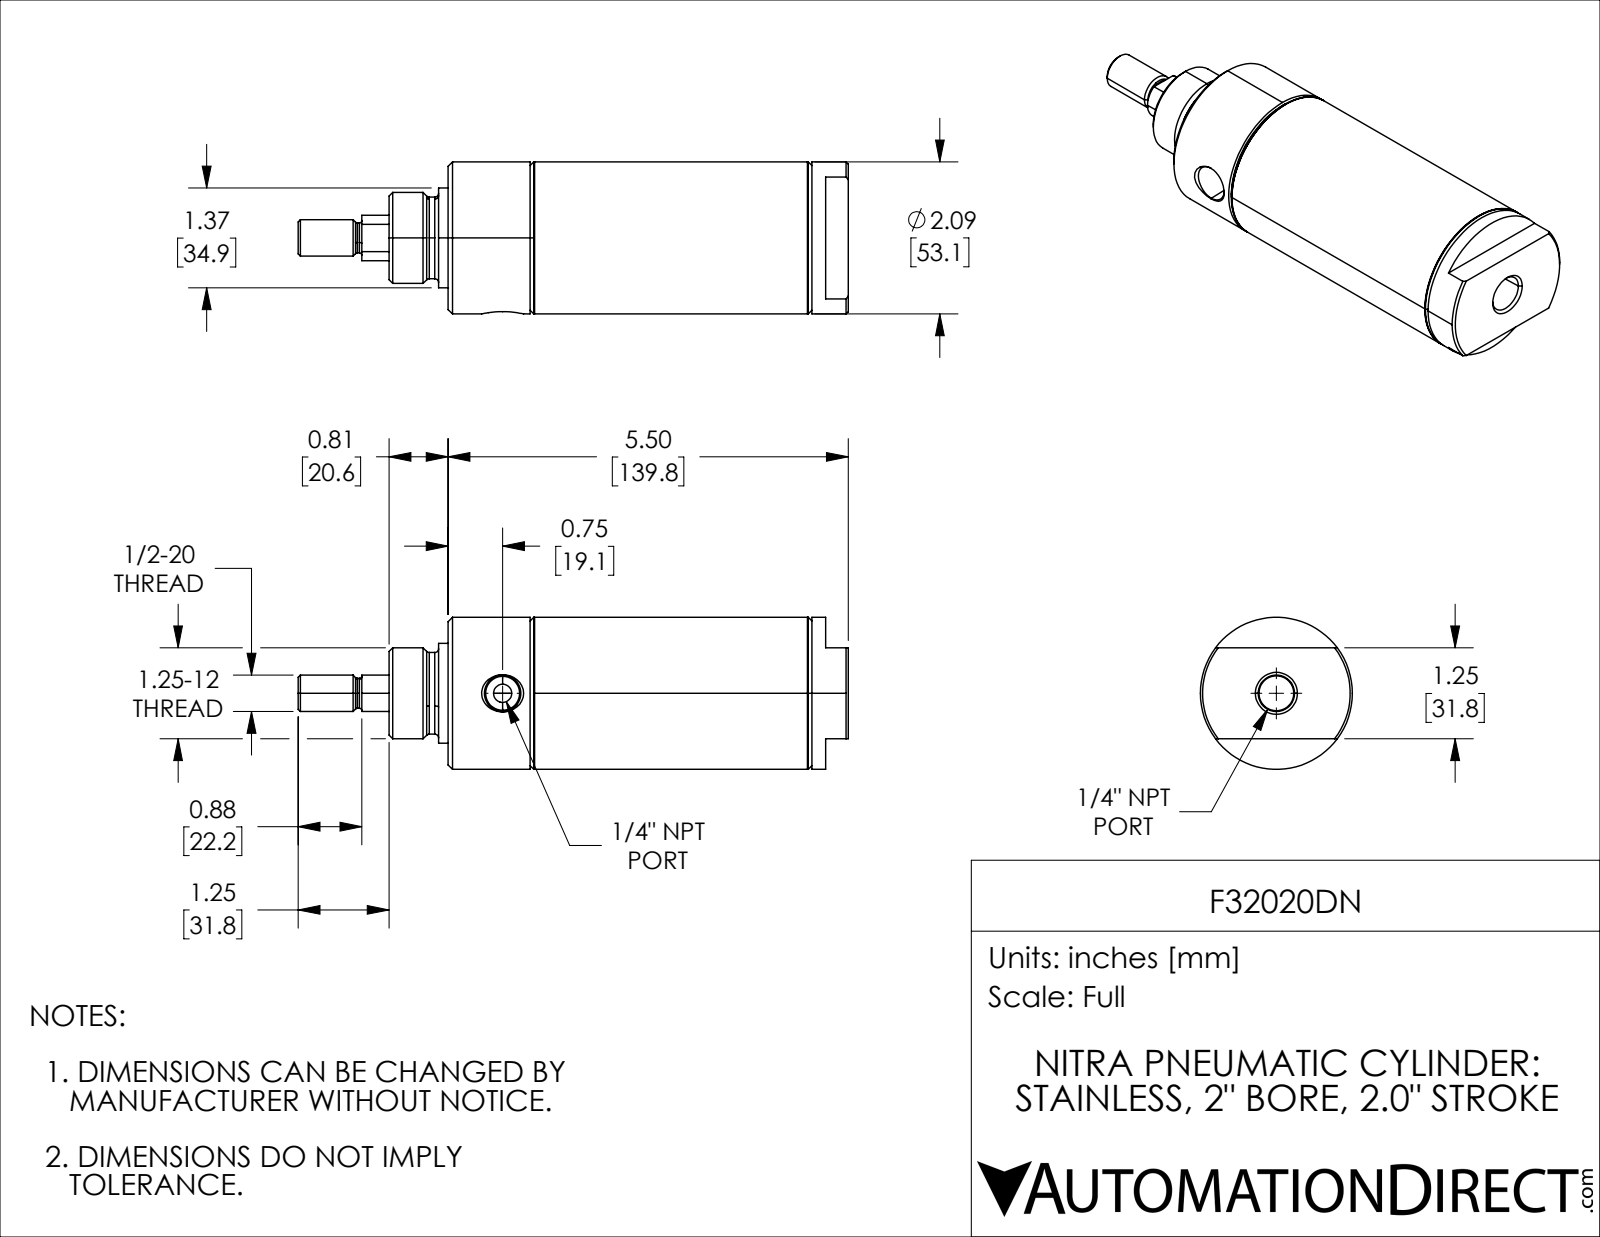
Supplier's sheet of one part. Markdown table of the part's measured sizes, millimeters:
| quantity | value |
| --- | --- |
| part name | F32020DN; F32020DN_3; F32020DN_9; F32020DN_5 (+1 more) |
| STEP written by | SolidWorks 2021 (CONFIG_CONTROL_DESIGN) |
| units | millimeters |
| bodies | 4 solids, 133 faces (25 planar, 46 cylindrical, 62 other) |
| overall size | 192.07 × 53.09 × 53.09 |
| volume | 219 069 mm³ |
| surface area | 74 452 mm² |
| round holes (diameter × count) | 6.35 × 1, 12.18 × 1, 16.52 × 1, 31.75 × 1, 49.05 × 1 |
| round bosses / shafts (diameter × count) | 53.09 × 1, 51.16 × 1, 34.87 × 1, 28.51 × 1, 15.88 × 1, 12.7 × 1, 10.46 × 1 |
| main face-to-face distances | 50.8, 30.17, 80.97, 101.6, 20.63, 38.15, 88.95, 119.12, 139.75, 12.7 |
